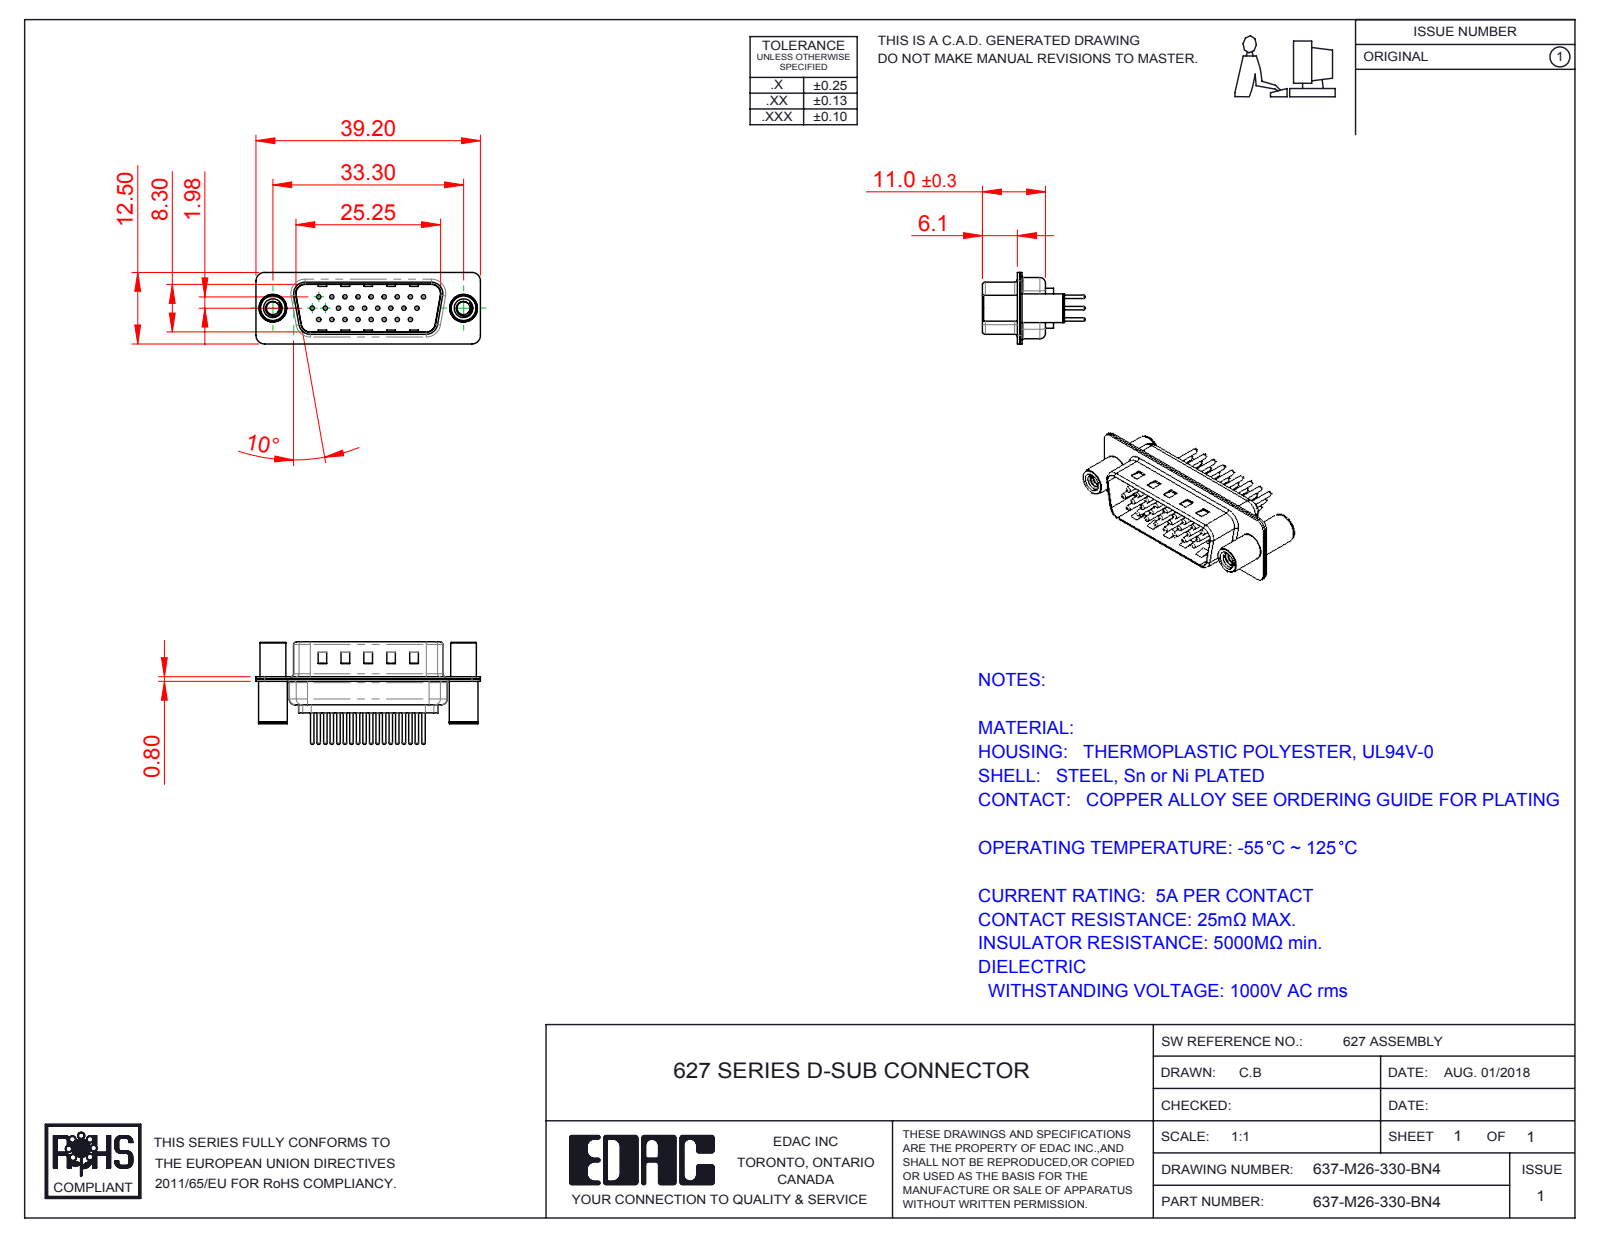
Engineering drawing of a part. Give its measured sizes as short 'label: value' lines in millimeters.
name: 637M Housing_26 Contacts; 637M Shell Front_26 Contacts; 637M Shell Rear_26 Contacts; 637M Contact Row 1_30 (+4 more)
written by: SolidWorks 2016 (CONFIG_CONTROL_DESIGN)
unit: mm
bodies: 31 solids, 1388 faces (327 planar, 549 cylindrical, 512 other)
size: 39.2 × 17.9 × 12.5
volume: 2 196 mm³; area: 6 280 mm²
holes: 26× ⌀0.75, 26× ⌀1.6, 26× ⌀2, 2× ⌀2.26, 2× ⌀3.26, 2× ⌀4, 2× ⌀4.8
bosses: 26× ⌀1.5, 26× ⌀0.6, 2× ⌀5, 2× ⌀4.9, 2× ⌀4.5
rounds: 16× R1.5, 12× R2, 8× R0.5, 8× R1.6, 4× R0.25, 4× R0.6, 4× R0.65, 4× R0.9
face distances: 0.4, 0.8, 9.5, 9.1, 8.7, 9.9, 6.3, 0.75, 5.5, 0.35
hole spacings: 3.96, 2.28, 4.57, 6.05, 2.29, 8.24, 6.86, 10.48
